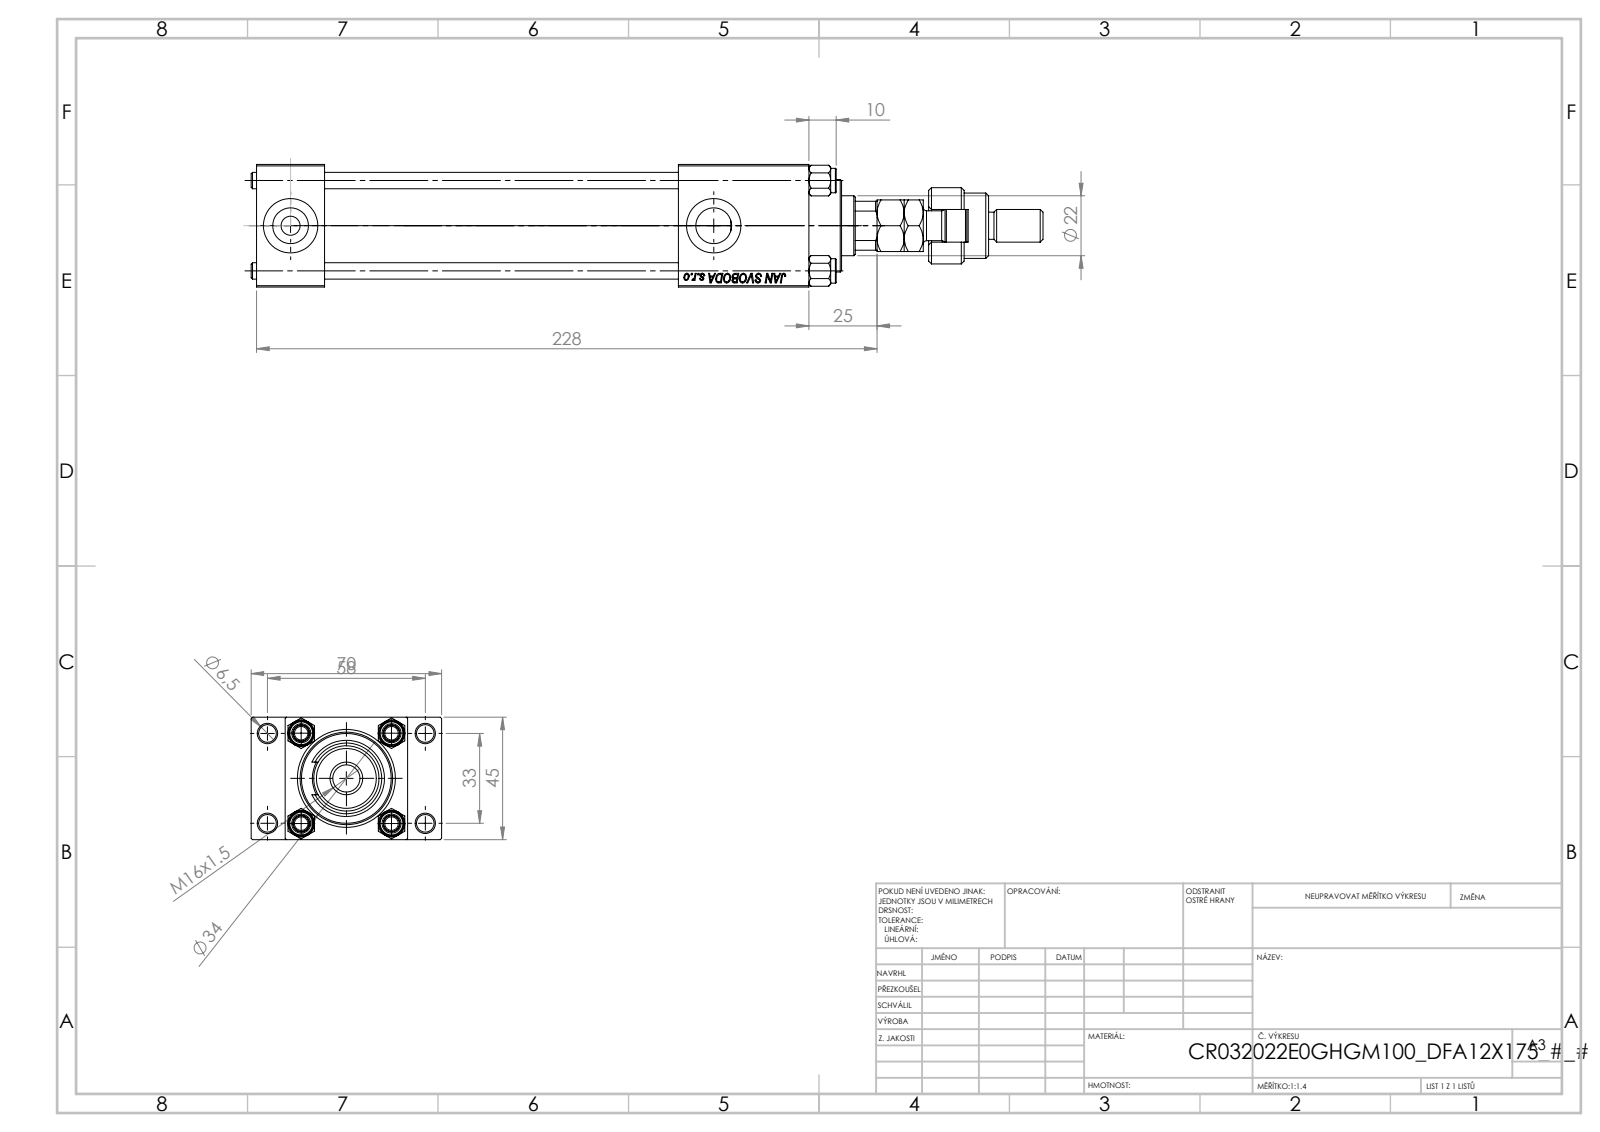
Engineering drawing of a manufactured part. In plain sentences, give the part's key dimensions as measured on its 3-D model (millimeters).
The part is named "V215CR_TYCINKA_E; V215CR_VCP_E; NUT_M5_E; FEMALE_PART_FOR_DFA (+3 more)". Its 3-D file was written by "SolidWorks 2019 (CONFIG_CONTROL_DESIGN)". It is 13 solids with 1220 faces: 525 planar, 99 cylindrical and 596 other. Overall it measures 291 by 70 by 45 millimeters. Its volume is 319 816 cubic millimeters and its surface area 117 142 square millimeters. Round holes: 4 of diameter 6, 4 of diameter 6.5, 2 of diameter 7, 2 of diameter 13.16, 2 of diameter 20, 1 of diameter 10.5, 1 of diameter 22, 1 of diameter 24, 1 of diameter 25, 1 of diameter 32, 1 of diameter 33. Round bosses or shafts: 4 of diameter 9, 1 of diameter 38, 1 of diameter 34, 1 of diameter 28, 1 of diameter 18, 1 of diameter 12, 1 of diameter 11, 1 of diameter 10. Partial cylindrical surfaces (rounded edges, fillets, slot ends): 1 of radius 9.75, 1 of radius 10.5. The main face-to-face distances are 45, 25, 12.5, 57.5, 203, 48, 155, 130, 178, 174.3. The hole center spacings are 12.4, 23.48, 33.2, 33.37, 35.35, 45.6, 56.35, 33.
